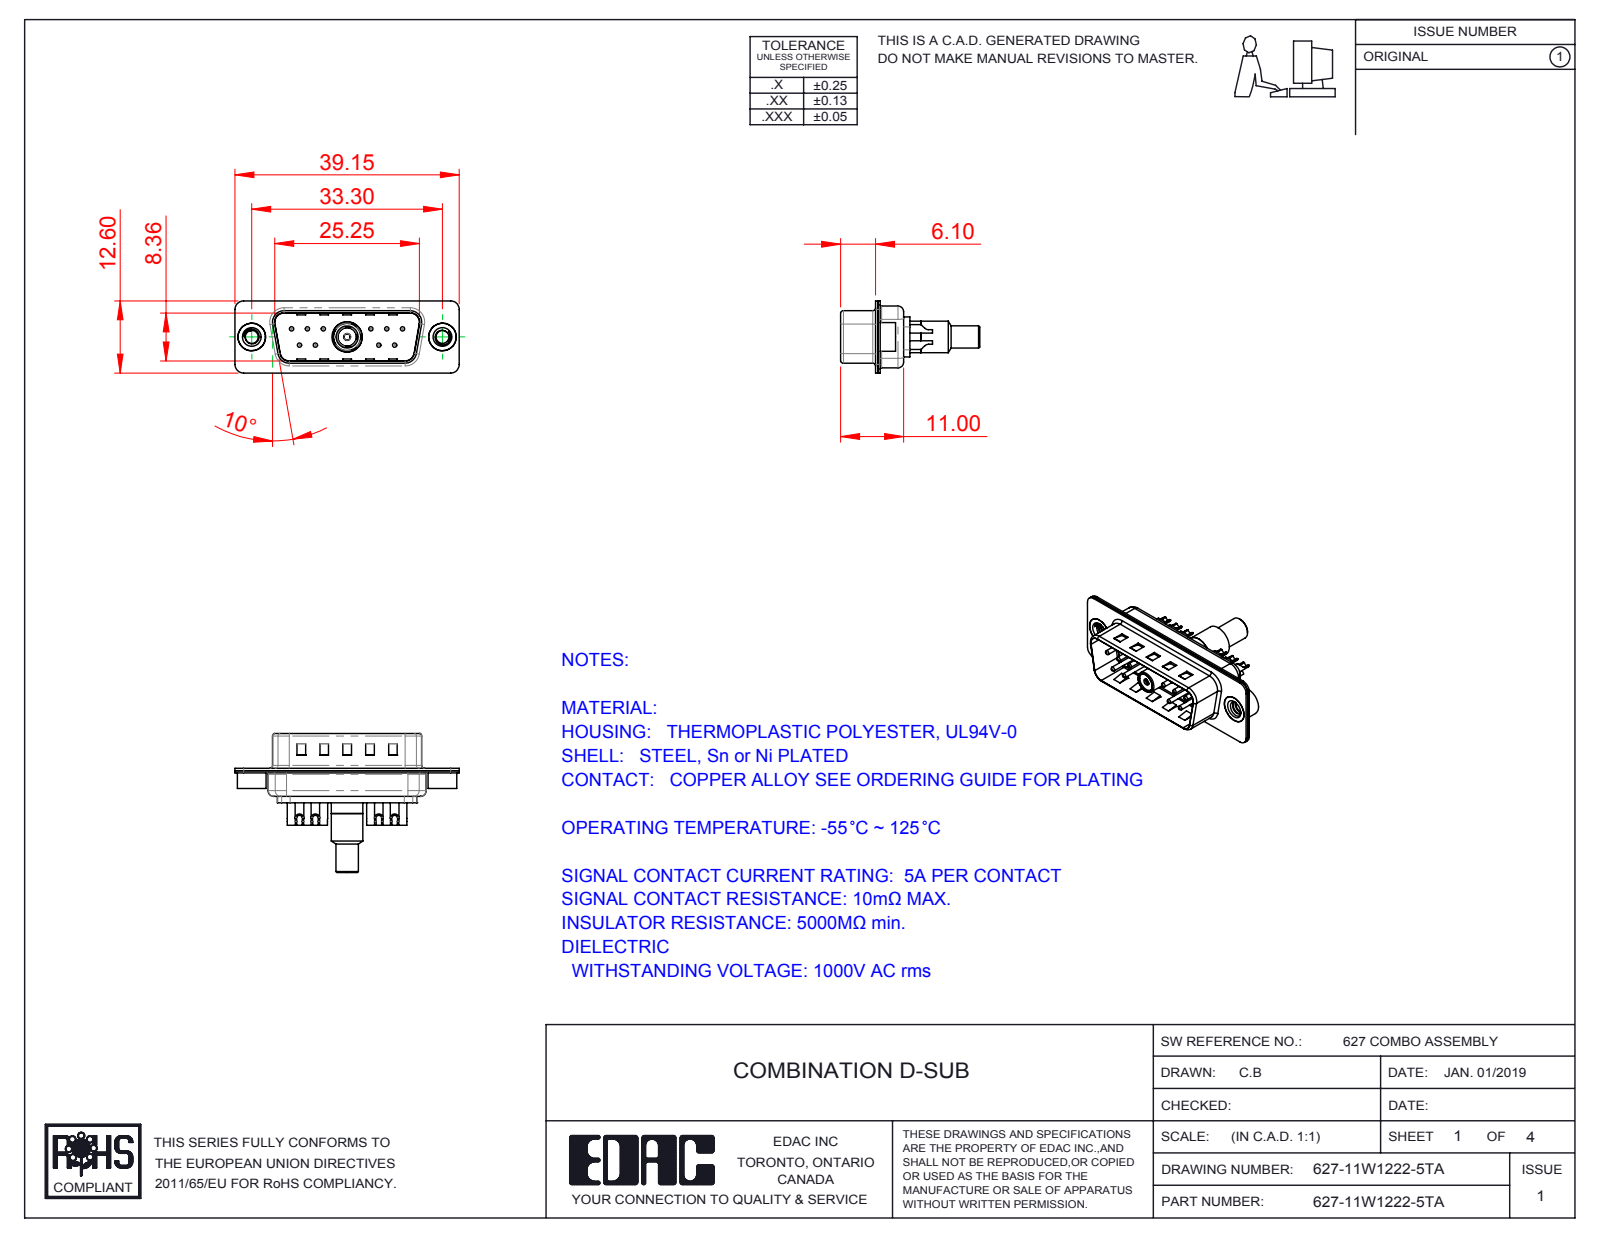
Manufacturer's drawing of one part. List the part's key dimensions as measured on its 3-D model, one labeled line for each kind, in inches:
Part name (STEP PRODUCT): Insulator Socket 2; Insulator Socket; Co-Ax Jack_Solder Cup Tail; 627Combo Threaded Rivet_A (+8 more)
STEP written by: SolidWorks 2016 (CONFIG_CONTROL_DESIGN)
Units: inches
Bodies: 21 solids, 852 faces (278 planar, 362 cylindrical, 212 other)
Overall size (bounding box): 1.541 × 0.957 × 0.496
Volume: 0.121 in³ · Surface area: 8.841 in²
Round holes (diameter × count): ⌀0.063 ×11, ⌀0.03 ×10, ⌀0.039 ×10, ⌀0.079 ×10, ⌀0.189 ×3, ⌀0.089 ×2, ⌀0.157 ×2, ⌀0.031 ×1, ⌀0.043 ×1, ⌀0.047 ×1, ⌀0.059 ×1, ⌀0.071 ×1
Round bosses / shafts (diameter × count): ⌀0.059 ×10, ⌀0.197 ×2, ⌀0.193 ×2, ⌀0.217 ×1, ⌀0.205 ×1, ⌀0.187 ×1, ⌀0.186 ×1, ⌀0.154 ×1
Partial cylindrical surfaces — rounded edges, fillets, slot ends (radius × count): R0.059 ×21, R0.079 ×12, R0.039 ×9, R0.02 ×8, R0.063 ×8, R0.01 ×4, R0.024 ×4, R0.026 ×4
Main face-to-face distances: 0.016, 0.032, 0.377, 0.345, 0.031, 0.059, 0.236, 0.055, 0.205, 0.22
Hole centre spacings: 0.124, 0.109, 0.545, 0.436, 0.654, 0.198, 0.198, 0.218
